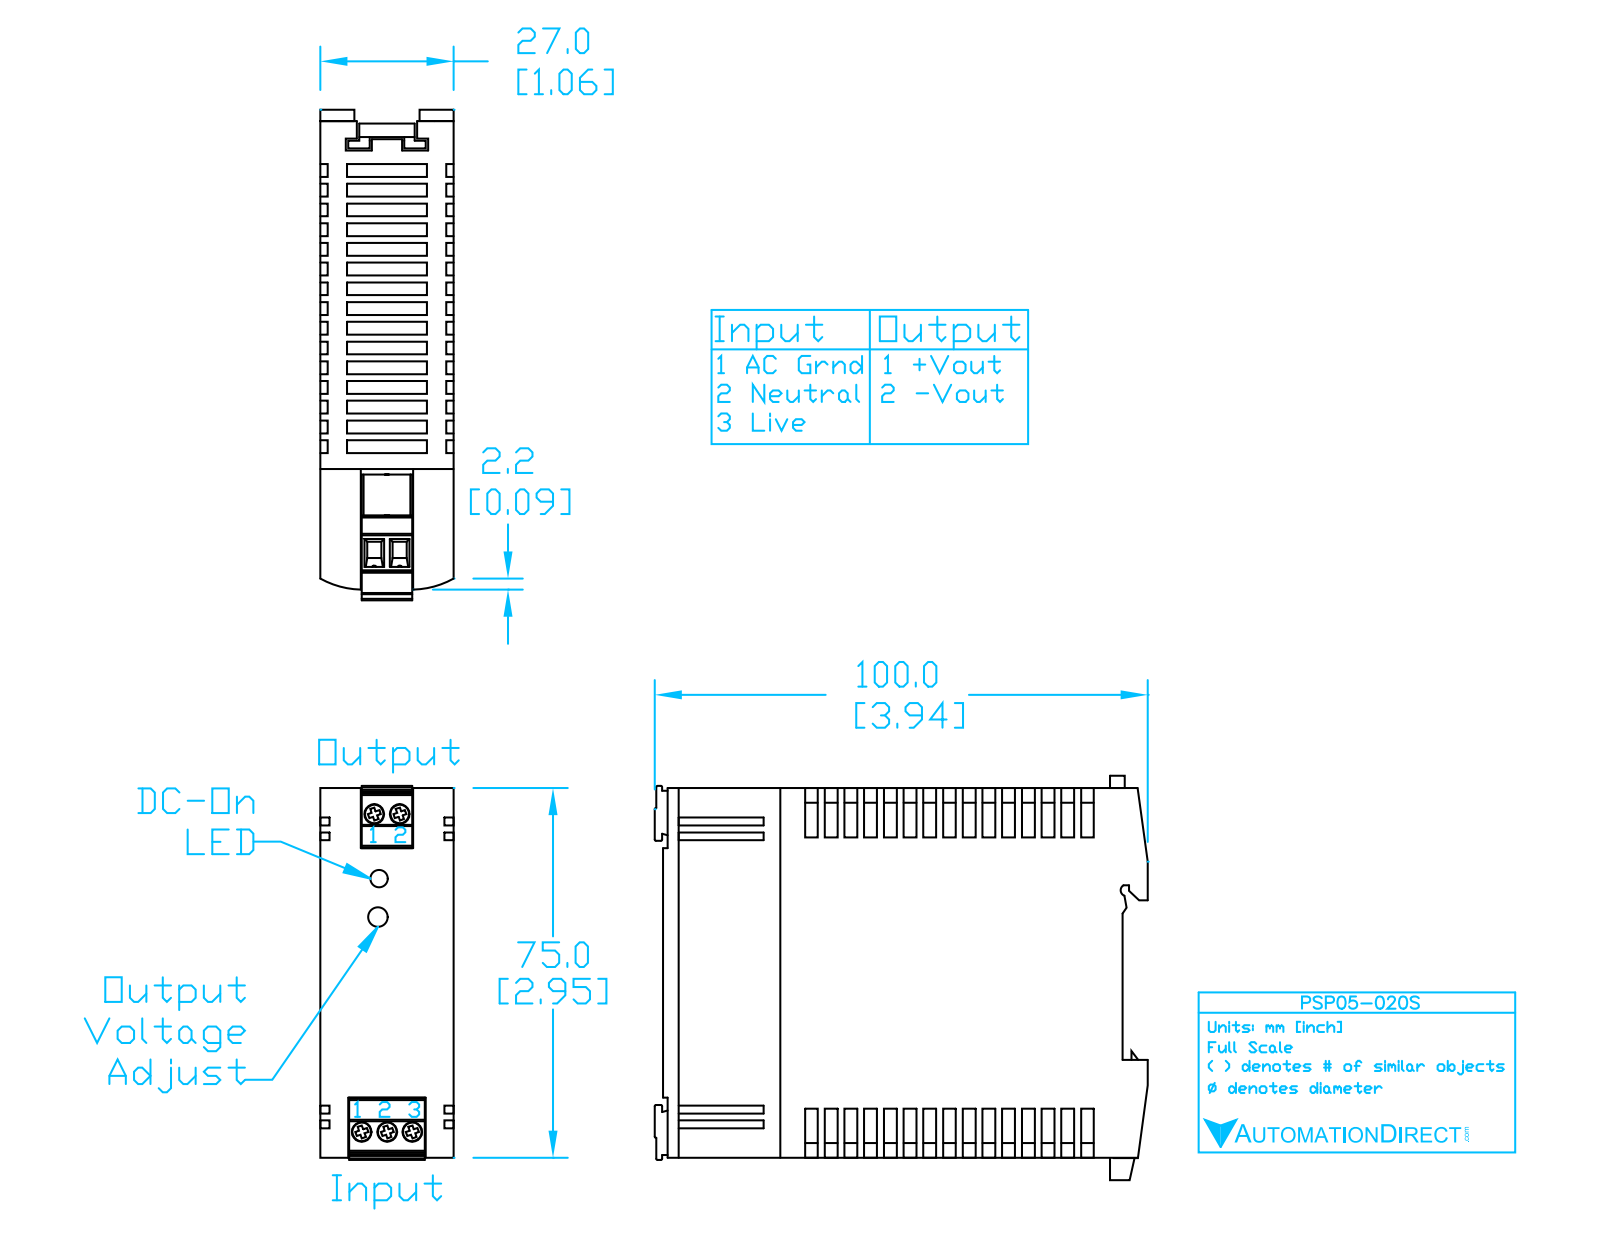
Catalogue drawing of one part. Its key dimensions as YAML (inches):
part_name: "PSP05-020S"
step_written_by: "SolidWorks 2011 (CONFIG_CONTROL_DESIGN)"
units: inches
bodies: {solids: 1, faces: 236, planar: 188, cylindrical: 0, other: 48}
overall_size: [4.026, 3.15, 1.063]
volume: 11.94
surface_area: 45.5
face_to_face_distances: [1.063, 2.953, 0.039, 0.207, 0.856, 0.467, 0.506, 2.028, 0.014, 2.494]
